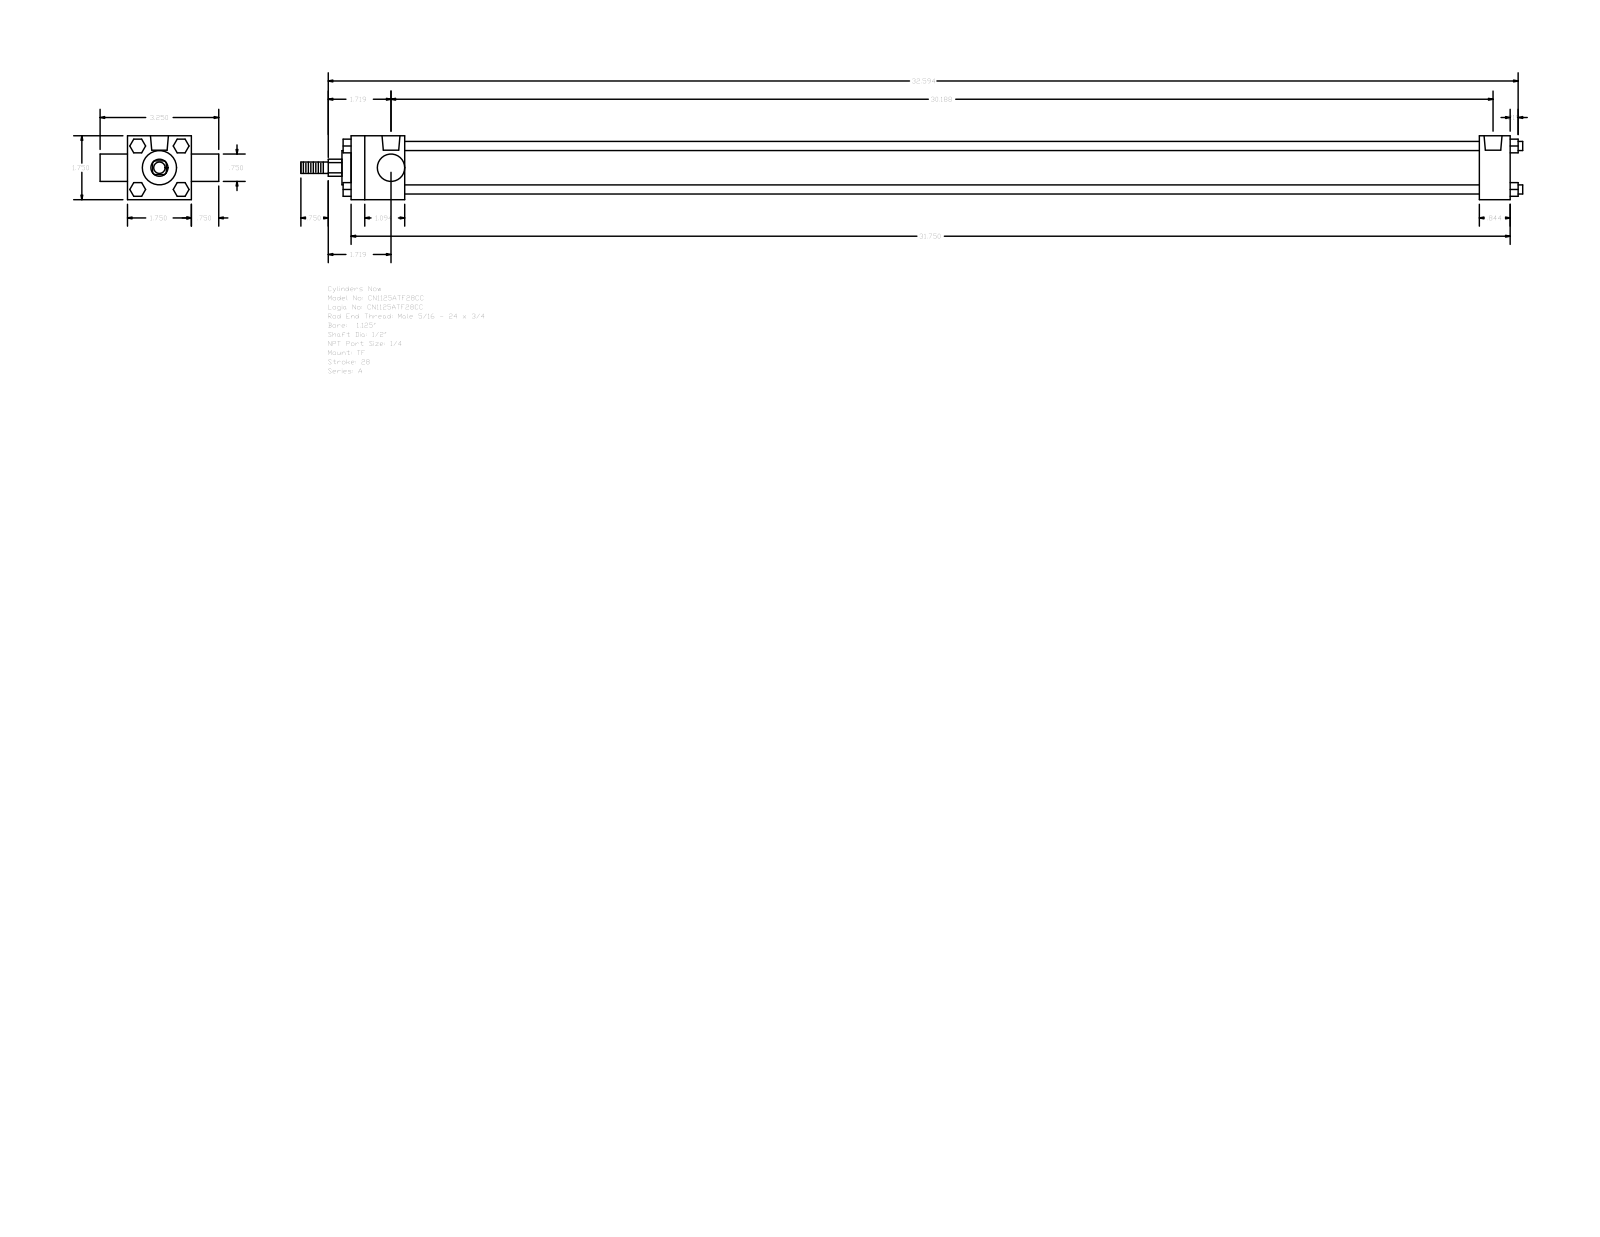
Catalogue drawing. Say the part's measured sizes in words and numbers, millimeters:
The part is named "A_TF__0112_0.5". Its 3-D file was written by "GSSL Pune (CONFIG_CONTROL_DESIGN)". It is 0 solids with 120 faces: 92 planar, 28 cylindrical and 0 other. Overall it measures 850.11 by 82.55 by 44.45 millimeters. Round holes: 3 of diameter 5.56, 2 of diameter 12.49. Round bosses or shafts: 4 of diameter 6.35, 1 of diameter 31.88, 1 of diameter 23.81, 1 of diameter 19.05, 1 of diameter 12.7, 1 of diameter 7.94. Partial cylindrical surfaces (rounded edges, fillets, slot ends): 1 of radius 5.94. The main face-to-face distances are 44.46, 806.45, 785.01, 21.44, 37.3, 747.71, 769.15, 19.04, 63.5, 9.53. The hole center spacings are 1.58, 1.59, 763.59, 765.17, 765.18, 766.76.
